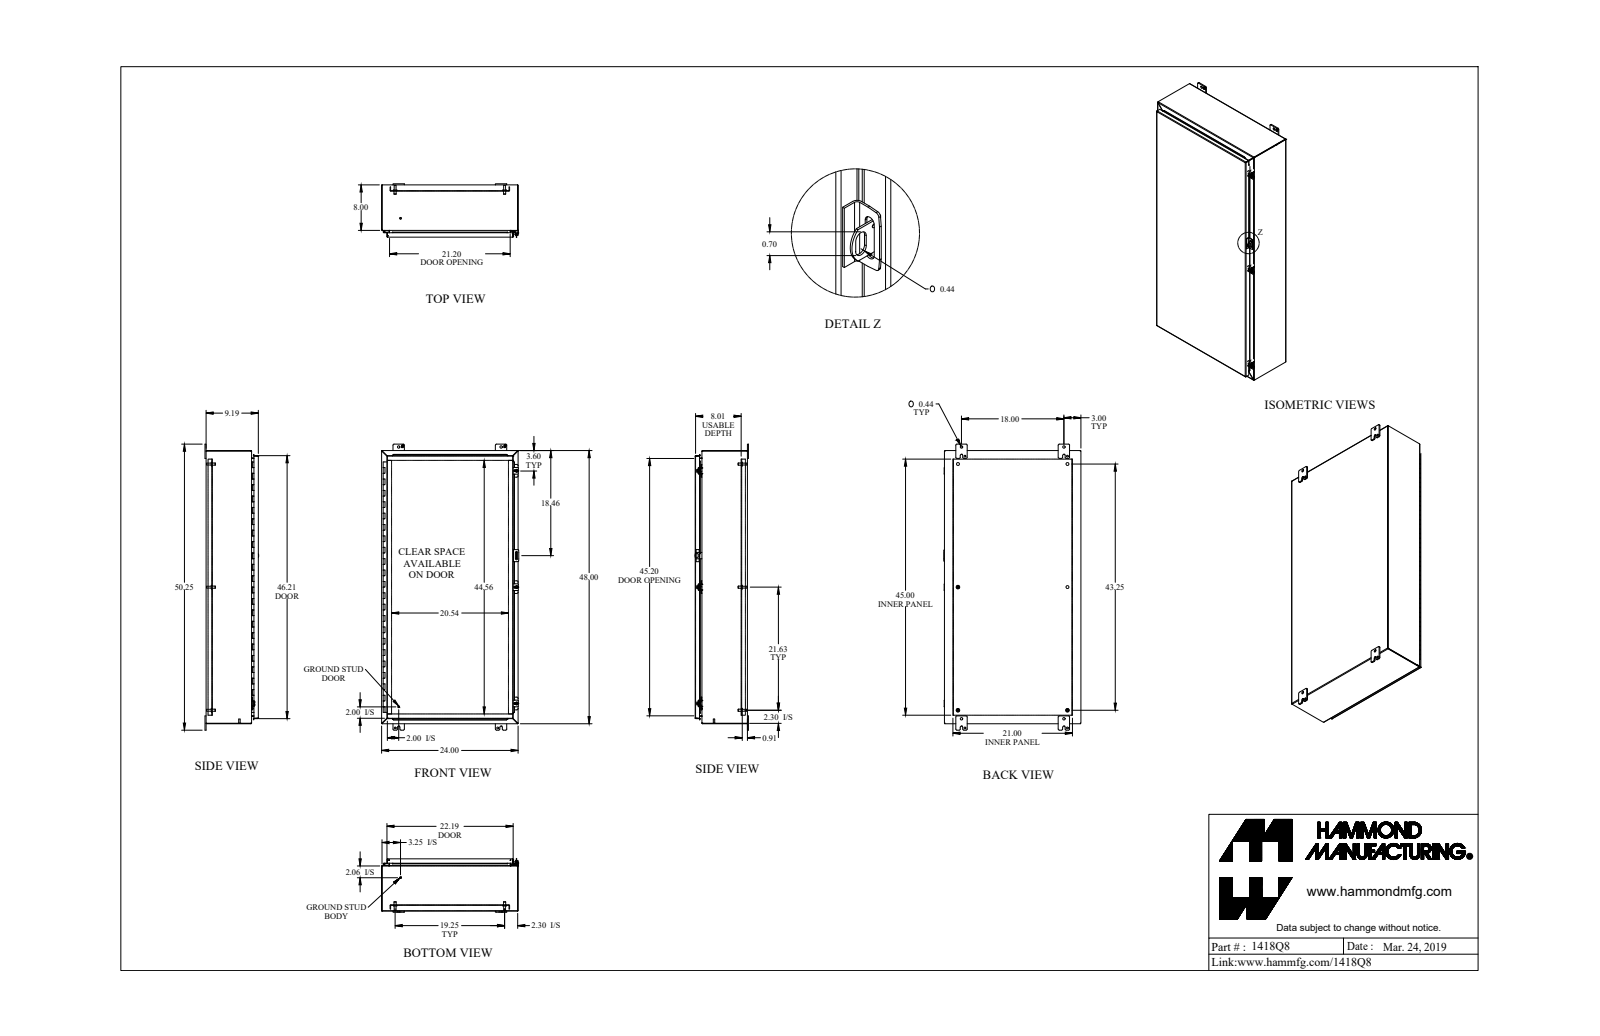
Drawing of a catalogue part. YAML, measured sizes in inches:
part_name: "1418Q8_Default"
step_written_by: "SolidWorks 2019 (CONFIG_CONTROL_DESIGN)"
units: inches
bodies: {solids: 48, faces: 1588, planar: 919, cylindrical: 575, other: 94}
overall_size: [50.25, 24.125, 9.437]
volume: 399.9
surface_area: 10331
round_holes:
  - {diameter: 0.5, count: 6}
  - {diameter: 0.307, count: 4}
  - {diameter: 0.313, count: 4}
  - {diameter: 0.437, count: 4}
  - {diameter: 0.213, count: 3}
  - {diameter: 0.265, count: 3}
  - {diameter: 0.375, count: 3}
  - {diameter: 0.445, count: 2}
  - {diameter: 0.445, count: 2}
  - {diameter: 0.125, count: 1}
  - {diameter: 0.187, count: 1}
round_bosses_or_shafts:
  - {diameter: 0.65, count: 6}
  - {diameter: 0.375, count: 6}
  - {diameter: 0.33, count: 6}
  - {diameter: 1, count: 4}
  - {diameter: 0.5, count: 3}
  - {diameter: 0.39, count: 3}
  - {diameter: 0.244, count: 3}
  - {diameter: 0.281, count: 2}
partial_cylinders:
  - {radius: 0.188, count: 26}
  - {radius: 0.036, count: 24}
  - {radius: 0.108, count: 24}
  - {radius: 0.048, count: 19}
  - {radius: 0.143, count: 19}
  - {radius: 0.25, count: 16}
  - {radius: 0.04, count: 8}
  - {radius: 0.218, count: 8}
face_to_face_distances: [0.072, 9.113, 9.041, 0.937, 9.185, 0.095, 1.009, 8.081, 8.009, 1.032]
hole_center_spacings: [19.25, 21.625, 28.952, 47.341, 1.735, 18, 47.75, 51.03]
